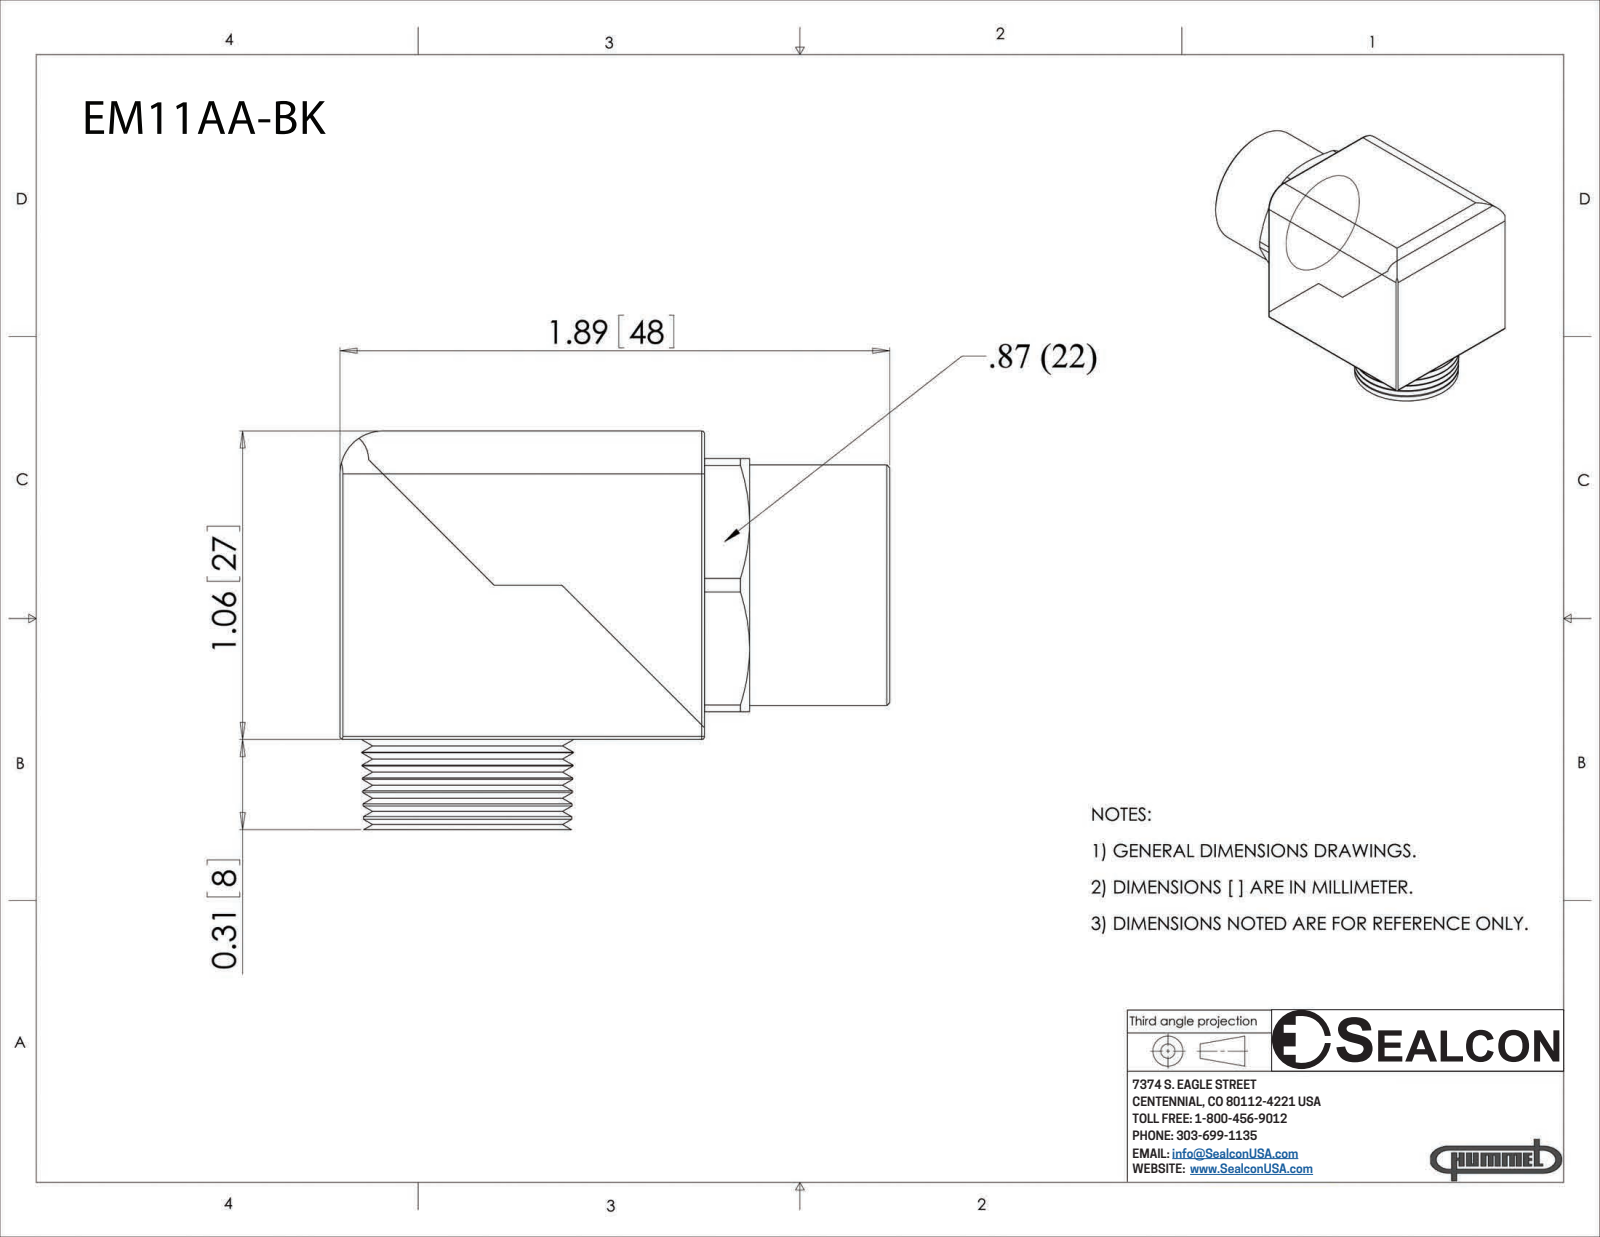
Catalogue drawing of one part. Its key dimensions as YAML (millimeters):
part_name: "EM11AA-BK"
step_written_by: "SolidWorks 2007 (AUTOMOTIVE_DESIGN)"
units: millimeters
bodies: {solids: 2, faces: 126, planar: 31, cylindrical: 34, other: 61}
overall_size: [48, 34.8, 26.9]
volume: 23470
surface_area: 10770
round_holes:
  - {diameter: 10.2, count: 2}
  - {diameter: 18.5, count: 1}
round_bosses_or_shafts:
  - {diameter: 21, count: 1}
partial_cylinders:
  - {radius: 0.3, count: 7}
  - {radius: 3.7, count: 3}
  - {radius: 2.5, count: 1}
  - {radius: 12.4, count: 1}
face_to_face_distances: [26.9, 4.2, 31.8, 13.5, 3.9, 35.8, 7.9, 21.3, 34.8, 22.1]
